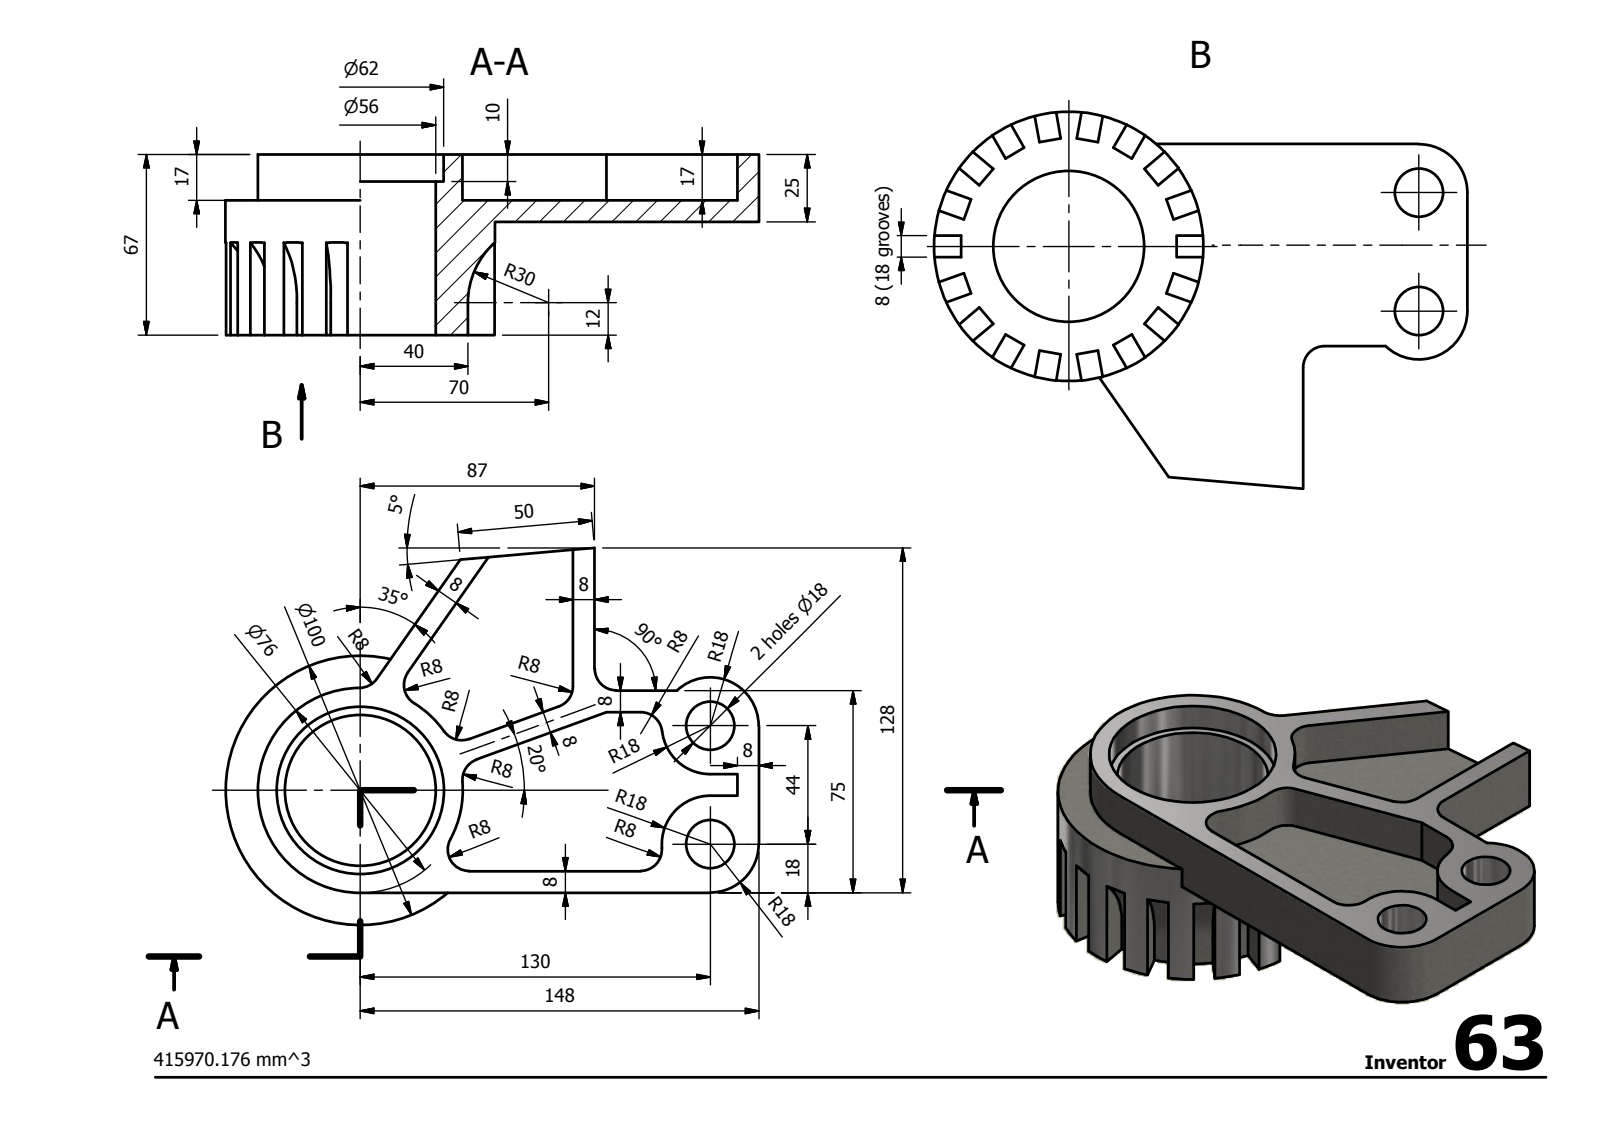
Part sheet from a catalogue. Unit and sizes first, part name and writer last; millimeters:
Units: millimetres
Overall size (bounding box): 198 × 140 × 67
Round holes (diameter × count): ⌀18 ×2, ⌀56 ×1, ⌀62 ×1
Round bosses / shafts (diameter × count): ⌀100 ×1
Partial cylindrical surfaces — rounded edges, fillets, slot ends (radius × count): R30 ×18, R8 ×9, R18 ×2, R38 ×1
Main face-to-face distances: 8, 25, 17, 67, 42, 50, 8.01, 7.98, 61, 34
Hole centre spacings: 44, 131.53, 132.2
Volume: 415 969 mm³ · Surface area: 89 902 mm²
Bodies: 1 solid, 115 faces (76 planar, 39 cylindrical, 0 other)
STEP written by: Autodesk Inventor 2014 (AUTOMOTIVE_DESIGN)
